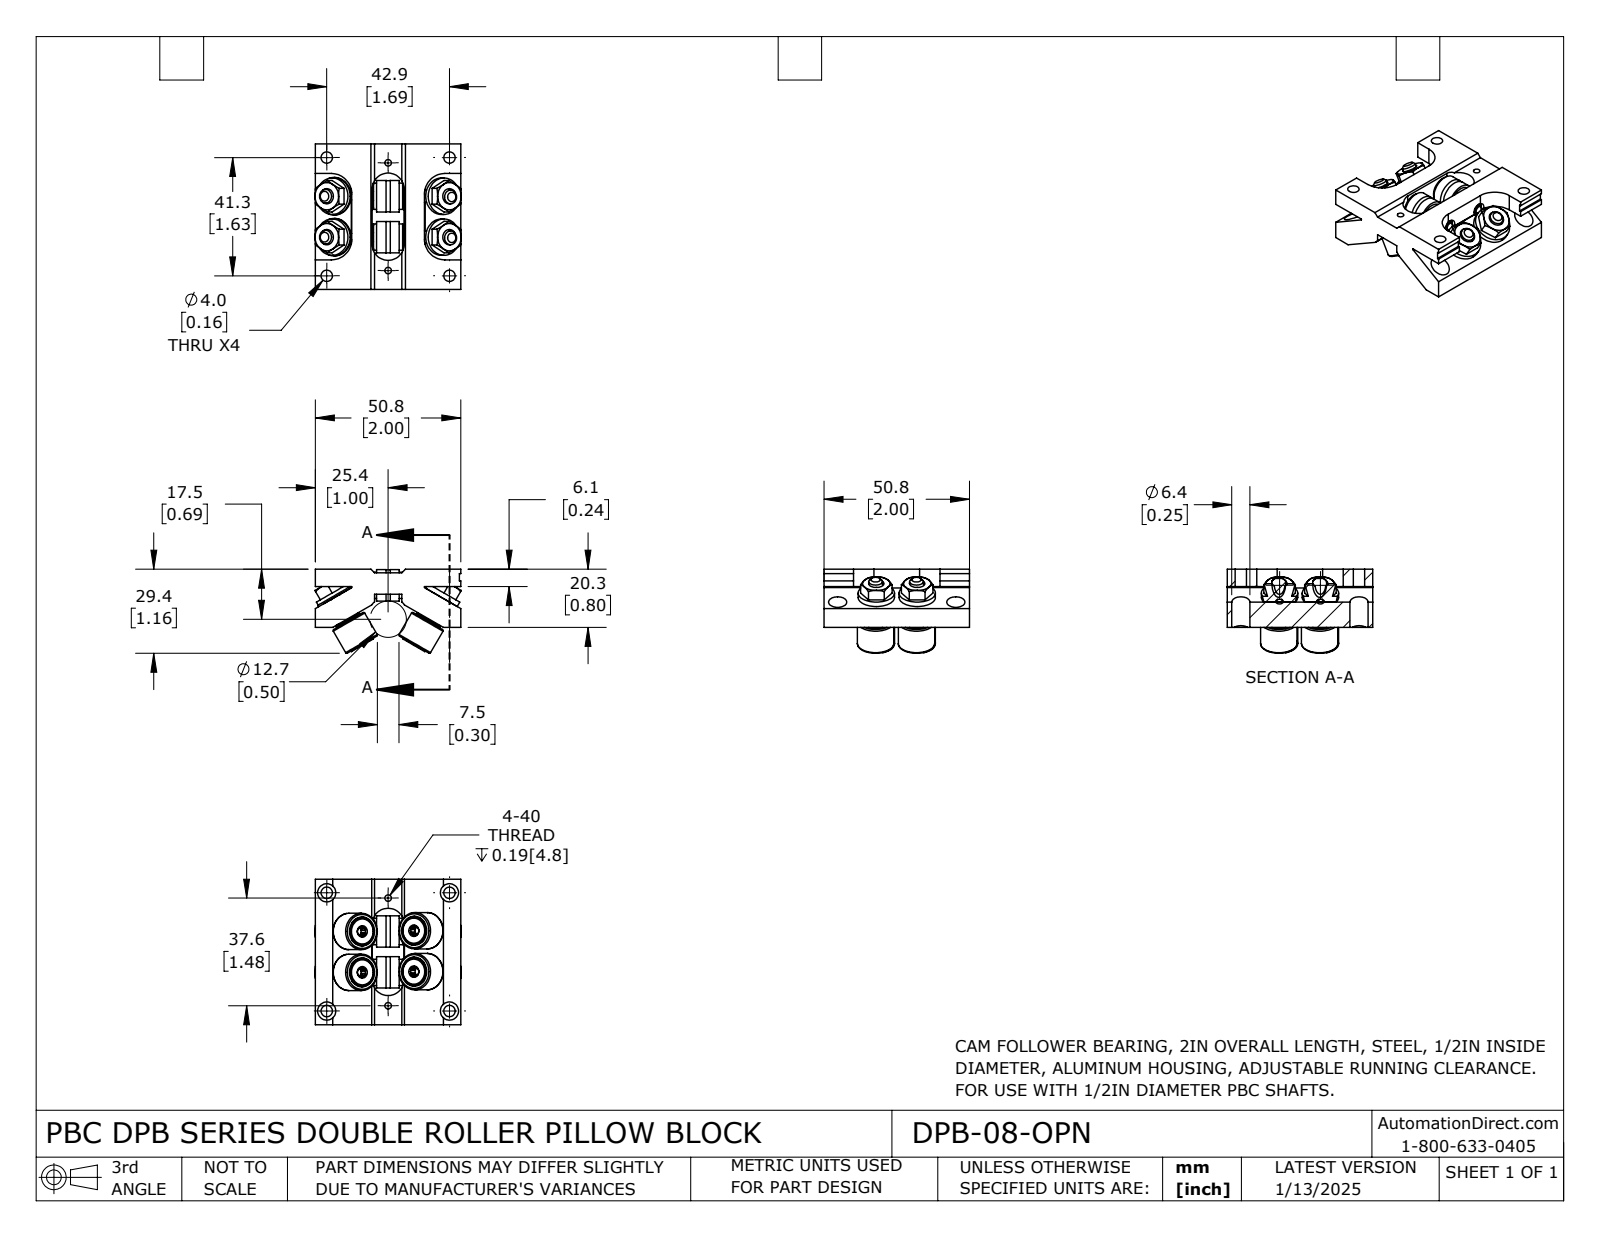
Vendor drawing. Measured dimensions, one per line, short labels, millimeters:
name: DPB-08-OPN
written by: SolidWorks 2023 (CONFIG_CONTROL_DESIGN)
unit: mm
bodies: 19 solids, 547 faces (230 planar, 181 cylindrical, 136 other)
size: 51.1 × 50.8 × 29.4
volume: 35 400 mm³; area: 19 820 mm²
holes: 4× ⌀3.3, 4× ⌀3.8, 4× ⌀4, 4× ⌀6.4, 4× ⌀10.1, 2× ⌀2.3, 2× ⌀3.2, 2× ⌀3.2, 2× ⌀4.8, 2× ⌀4.8, 2× ⌀4.9, 2× ⌀5.1
bosses: 6× ⌀12.7, 4× ⌀9.4, 2× ⌀13.1, 2× ⌀11, 2× ⌀9.2, 2× ⌀6.4, 2× ⌀5.1, 2× ⌀4.8
rounds: 4× R7.1, 2× R5.6, 1× R7.1
face distances: 50.8, 8.7, 8.7, 6.1, 14.2, 20.3, 19.8, 31, 10.3, 9.5
hole spacings: 14.3, 0.4, 21.5, 44.9, 0.4, 14, 14.5, 41.3
